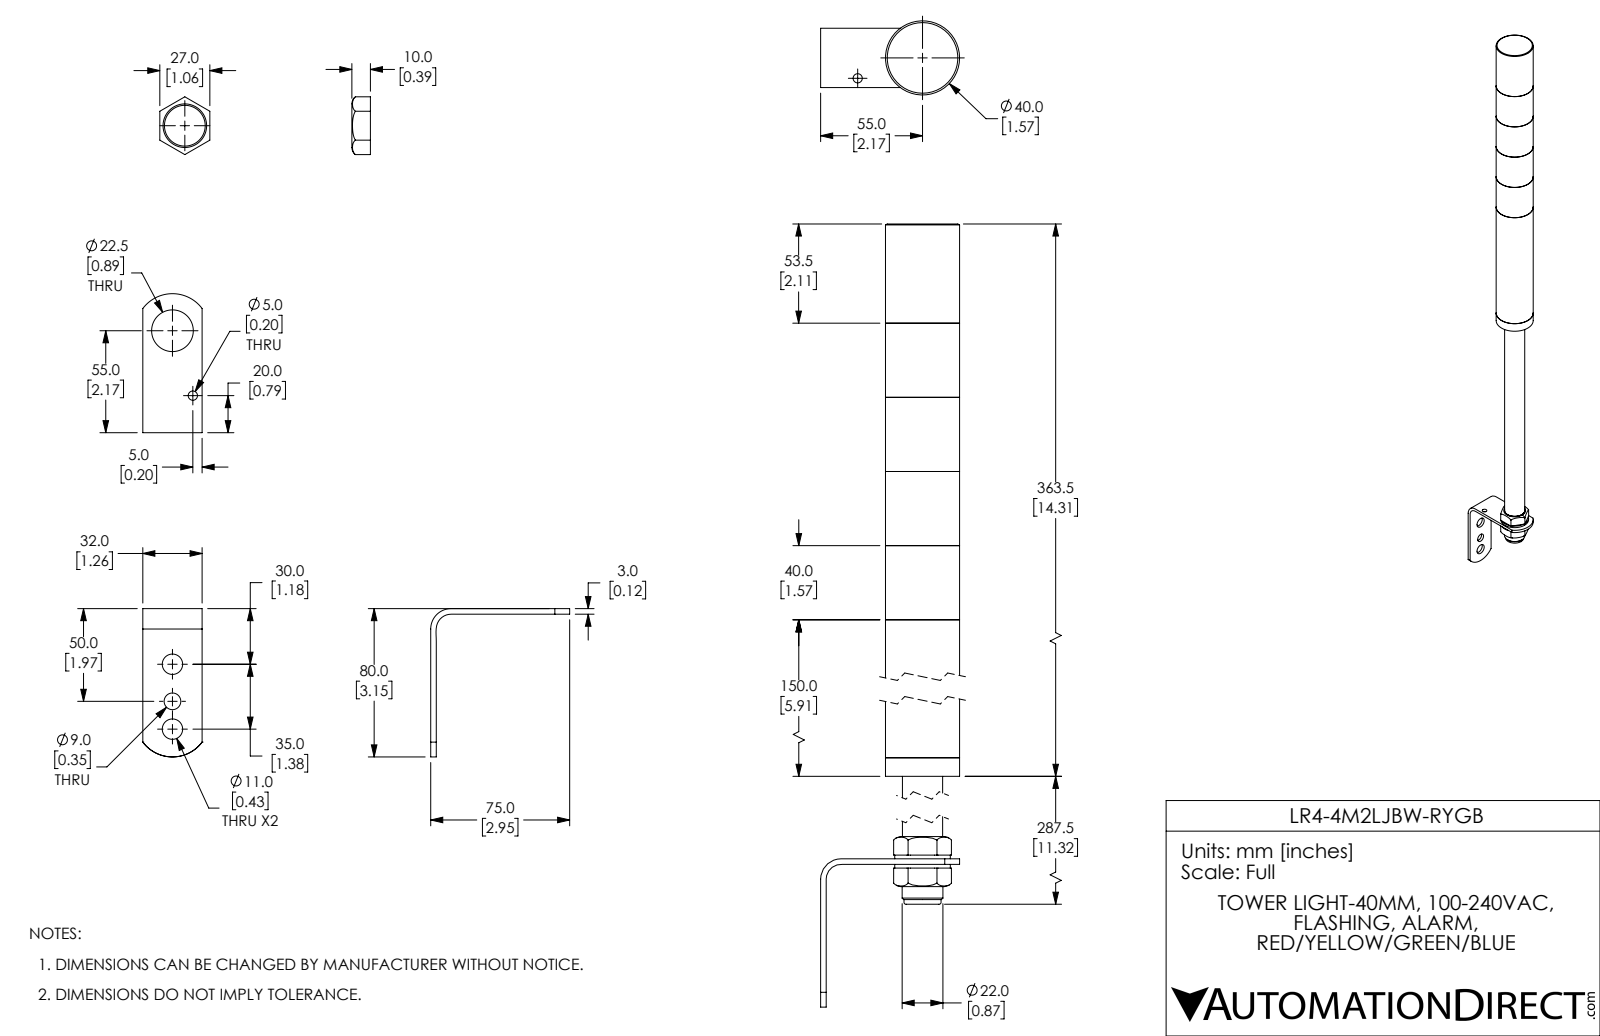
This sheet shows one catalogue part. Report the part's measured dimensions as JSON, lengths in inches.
{"part_name": "LR4-4M2LJBW-RYGB", "step_written_by": "SolidWorks 2017 (AUTOMOTIVE_DESIGN)", "units": "inches", "bodies": {"solids": 13, "faces": 175, "planar": 64, "cylindrical": 97, "other": 14}, "overall_size": [27.815, 2.953, 1.575], "volume_in3": 31.82, "surface_area_in2": 210, "round_holes": [[0.126, 2], [0.433, 2], [0.197, 1], [0.303, 1], [0.354, 1], [0.697, 1], [0.866, 1], [0.886, 1], [1.087, 1], [1.386, 1], [1.39, 1], [1.463, 1]], "round_bosses_or_shafts": [[1.575, 1], [1.461, 1], [1.366, 1], [1.181, 1], [0.854, 1]], "partial_cylinders_radius": [[0.787, 1]], "face_to_face_distances": [1.575, 3.15, 4.724, 6.311, 0.406, 1.98, 5.354, 6.929, 8.504, 10.079], "hole_center_spacings": [0.283, 0.567, 0.591, 0.787, 1.177, 1.378, 1.444, 1.717]}
